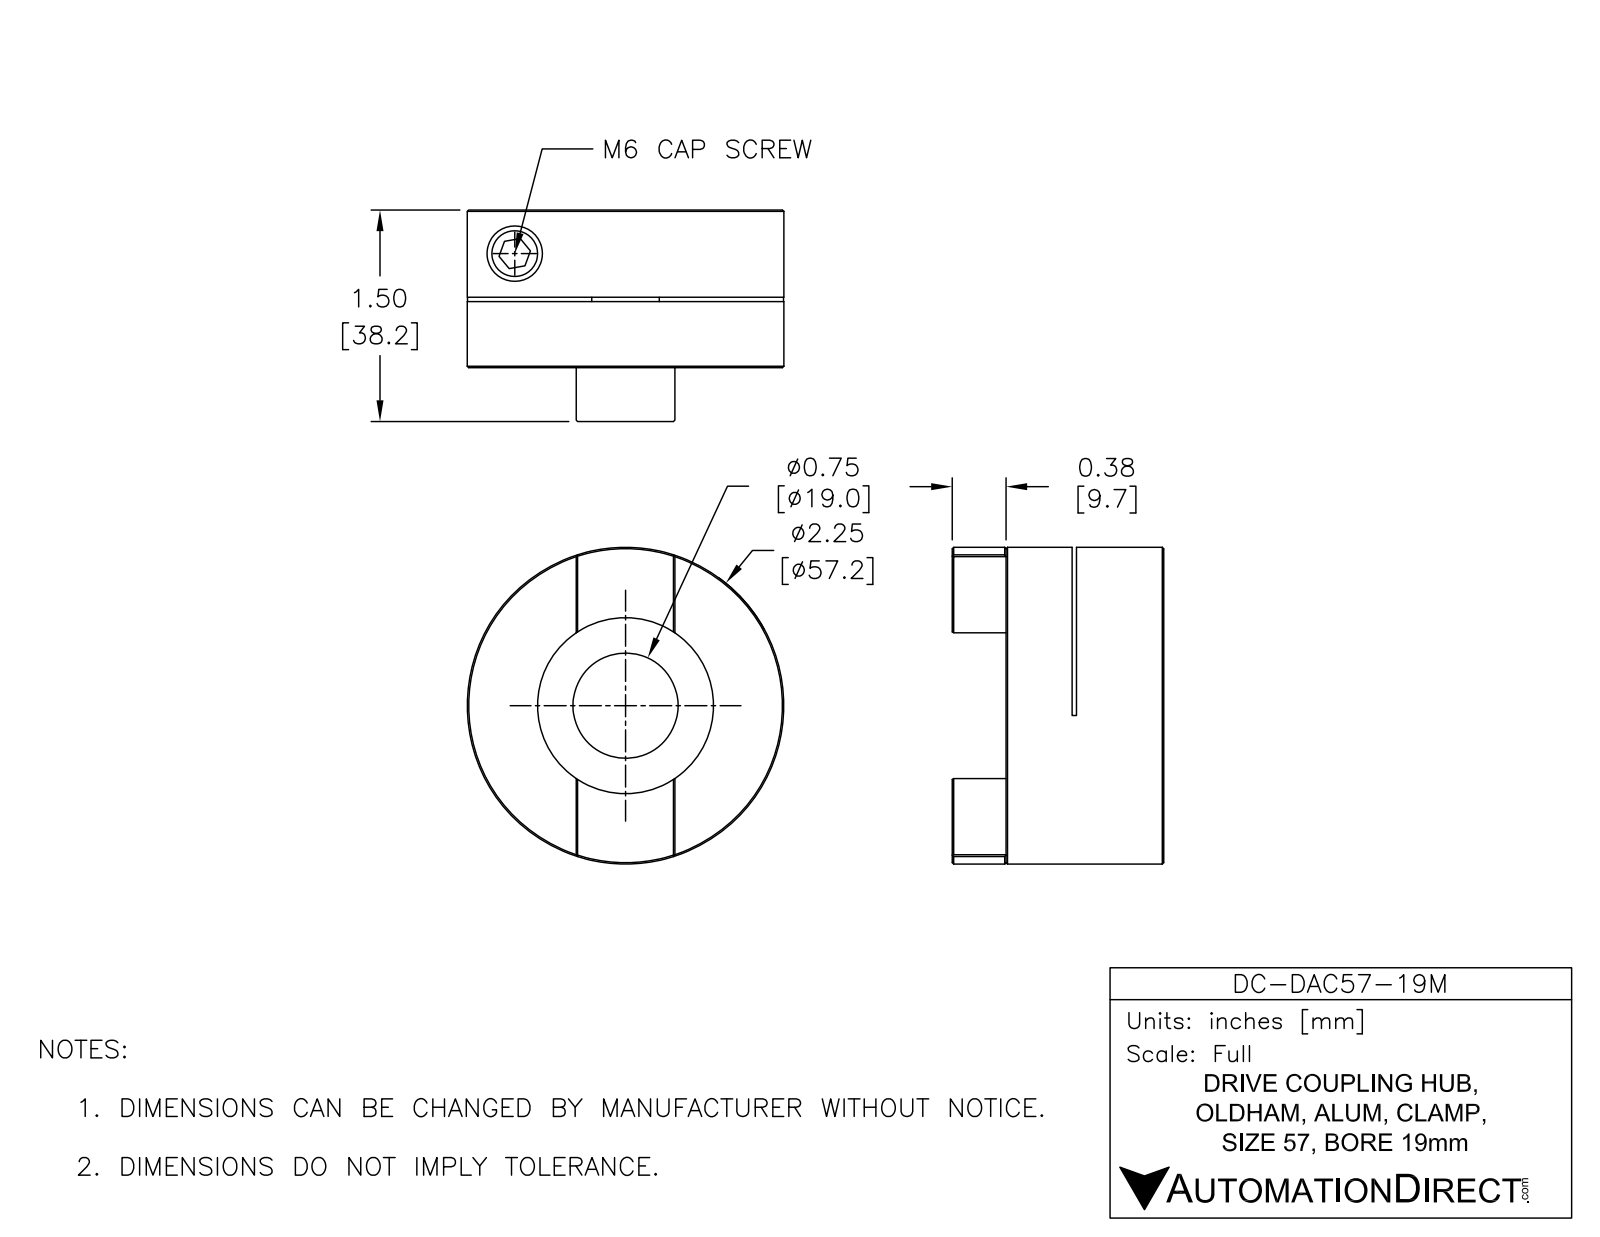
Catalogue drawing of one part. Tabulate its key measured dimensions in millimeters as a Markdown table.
| quantity | value |
| --- | --- |
| part name | DC-DAC57-19M |
| STEP written by | SolidWorks 2015 (AUTOMOTIVE_DESIGN) |
| units | millimeters |
| bodies | 1 solid, 55 faces (29 planar, 16 cylindrical, 10 other) |
| overall size | 57.15 × 57.15 × 38.16 |
| volume | 70 201 mm³ |
| surface area | 16 326 mm² |
| round holes (diameter × count) | 4.93 × 1, 6.6 × 1, 11 × 1, 12.7 × 1, 31.75 × 1 |
| round bosses / shafts (diameter × count) | 57.15 × 1 |
| main face-to-face distances | 16.54, 28.45, 11.91, 15.75, 0.79, 12.7, 28, 12.25, 11.46, 0.45 |
